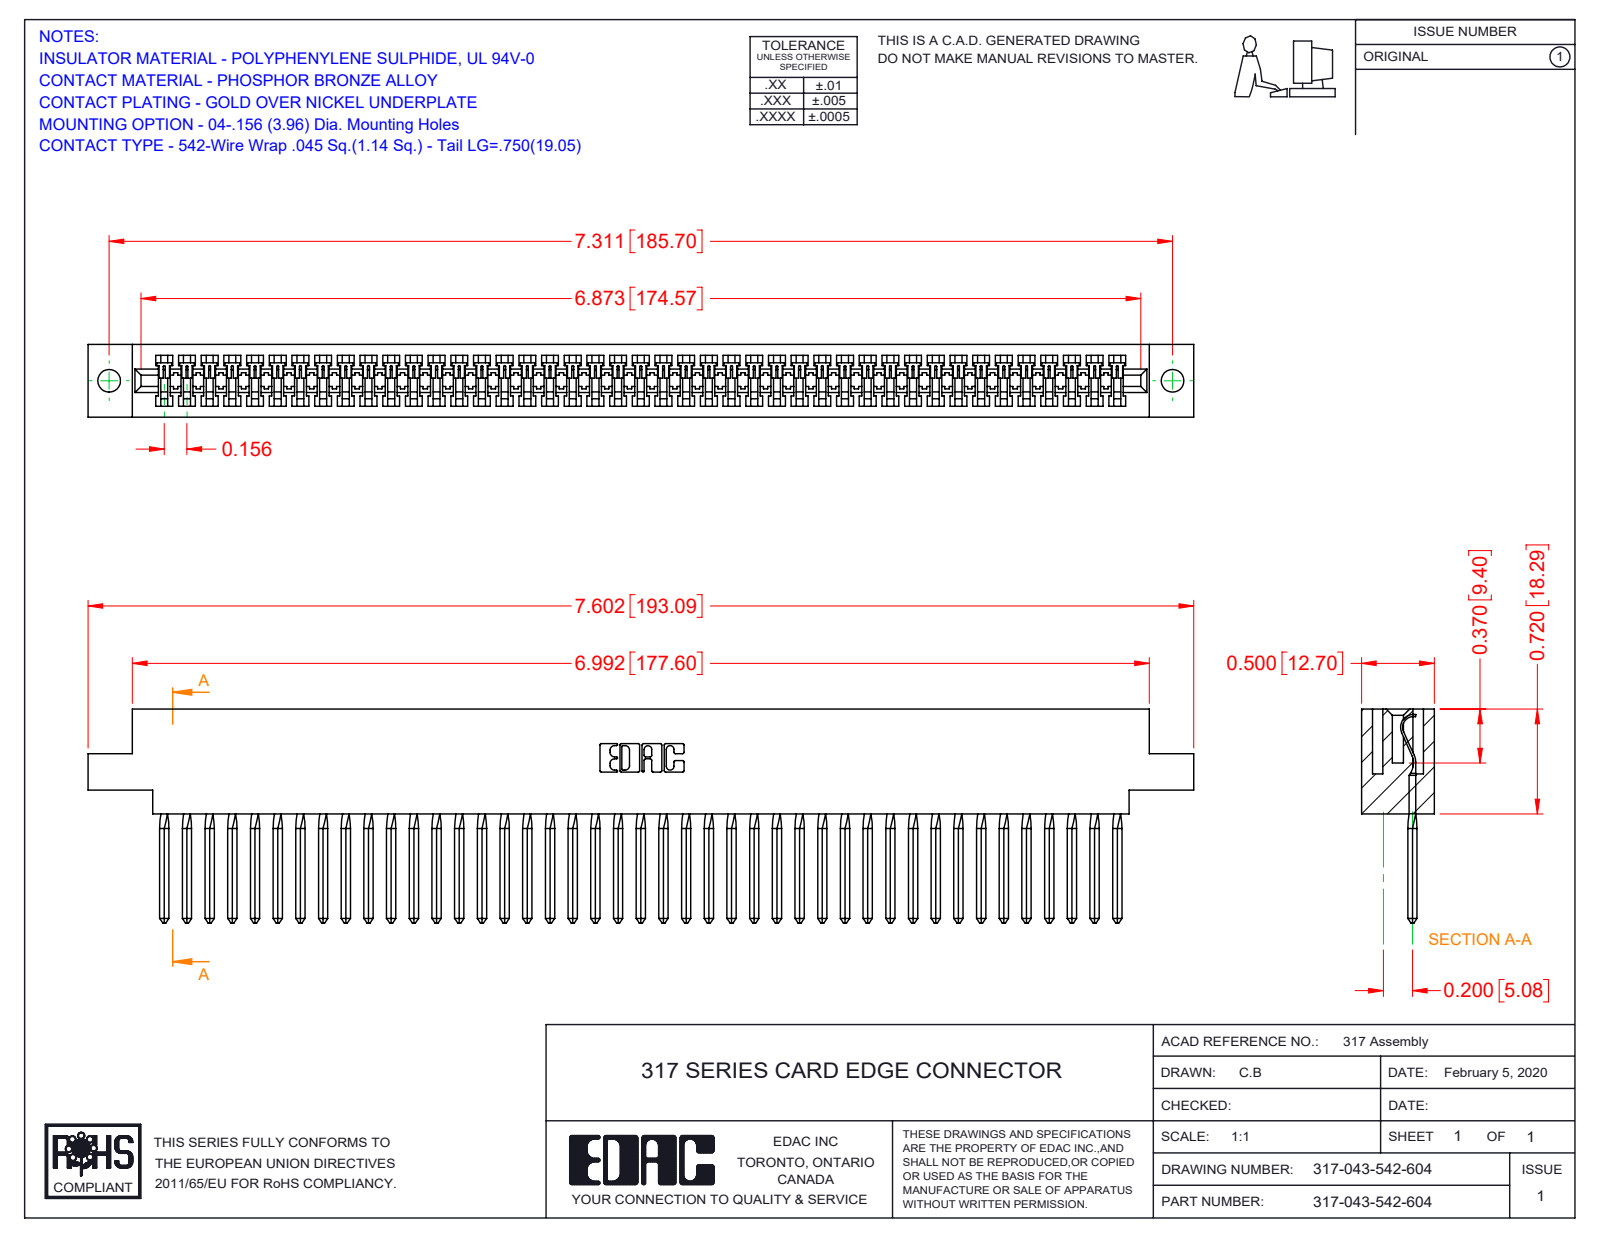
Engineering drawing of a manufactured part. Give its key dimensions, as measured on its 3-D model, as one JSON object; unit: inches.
{"part_name": "317-290-003_542; 317 Part_.156 Dia - TH; 317-043-542-604", "step_written_by": "SolidWorks 2016 (CONFIG_CONTROL_DESIGN)", "units": "inches", "bodies": {"solids": 44, "faces": 3327, "planar": 2810, "cylindrical": 345, "other": 172}, "overall_size": [7.602, 1.47, 0.5], "volume_in3": 1.816, "surface_area_in2": 56.01, "round_holes": [[0.156, 2]], "partial_cylinders_radius": [[0.006, 86], [0.01, 22], [0.007, 6], [0.031, 6], [0.026, 3], [0.074, 1], [0.089, 1], [0.1, 1]], "face_to_face_distances": [0.5, 0.075, 0.425, 0.35, 0.72, 0.136, 0.195, 0.211, 0.289, 0.213], "hole_center_spacings": [7.311]}
